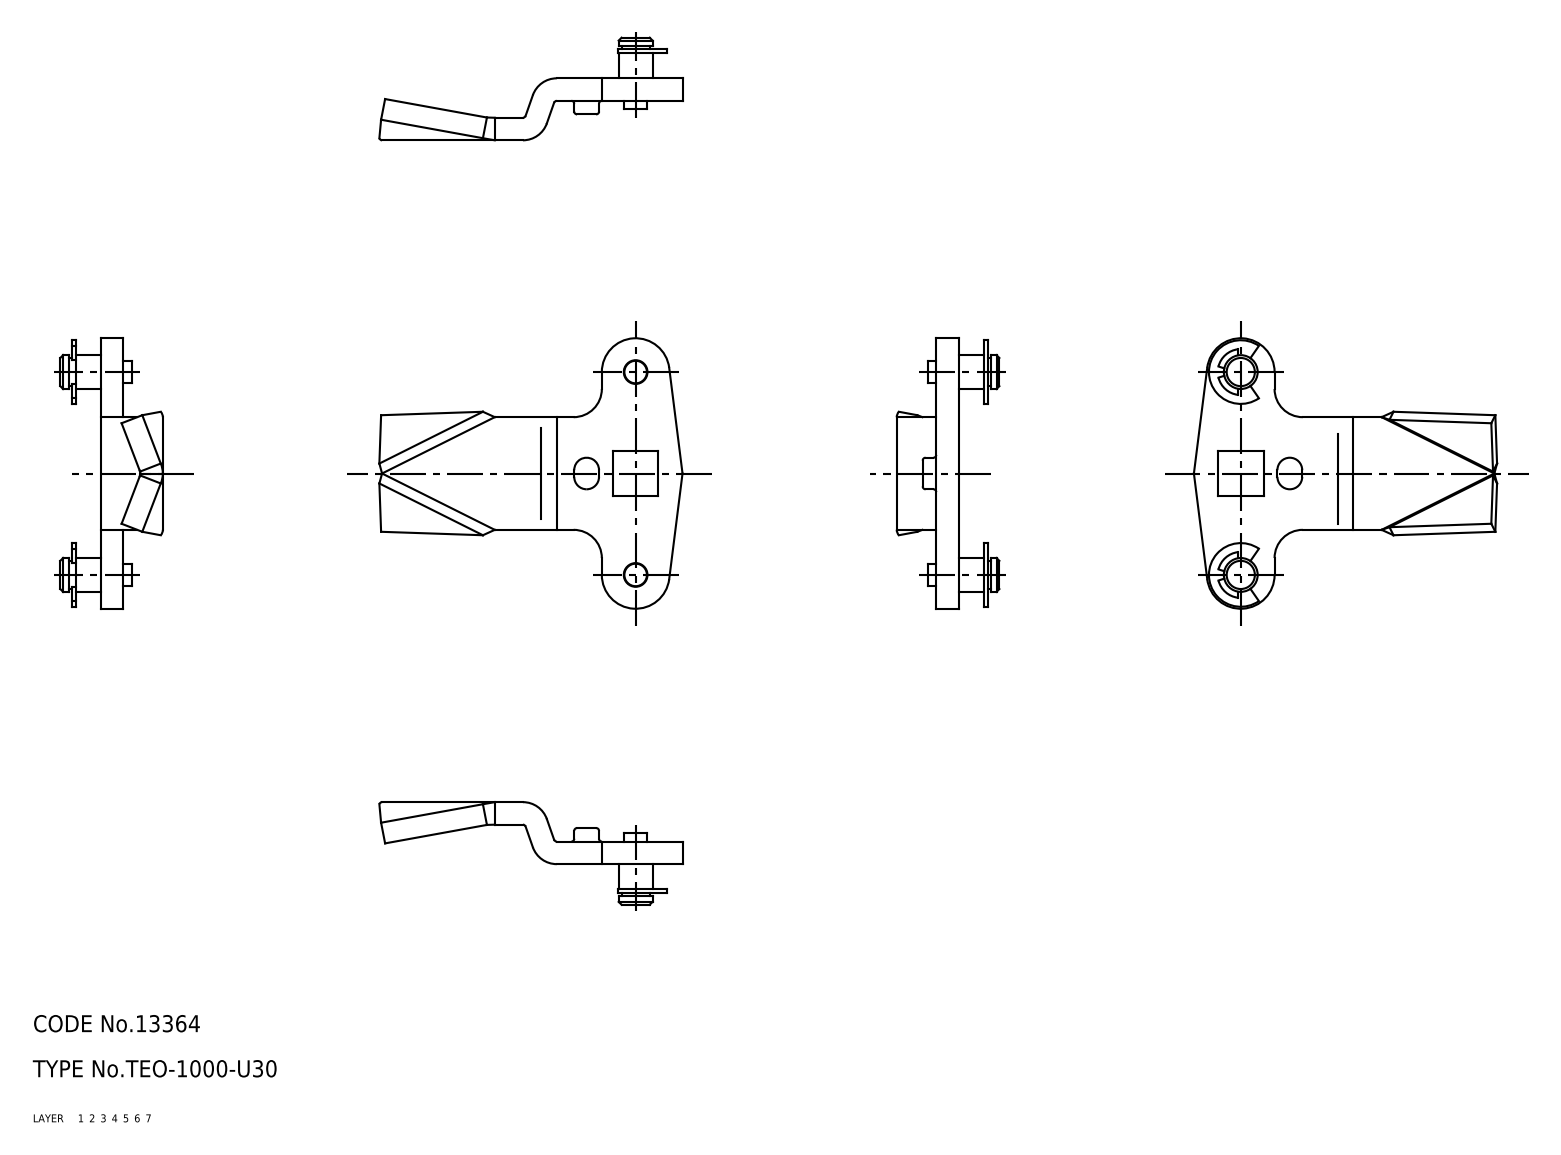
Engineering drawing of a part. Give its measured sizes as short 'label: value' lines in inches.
name: retainer; cam; TEO_1000_U30_31875_36
written by: CADfix (AUTOMOTIVE_DESIGN)
unit: in
bodies: 3 solids, 116 faces (0 planar, 0 cylindrical, 116 other)
size: 2.124 × 1.89 × 0.717
volume: 0.381 in³; area: 6.882 in²
